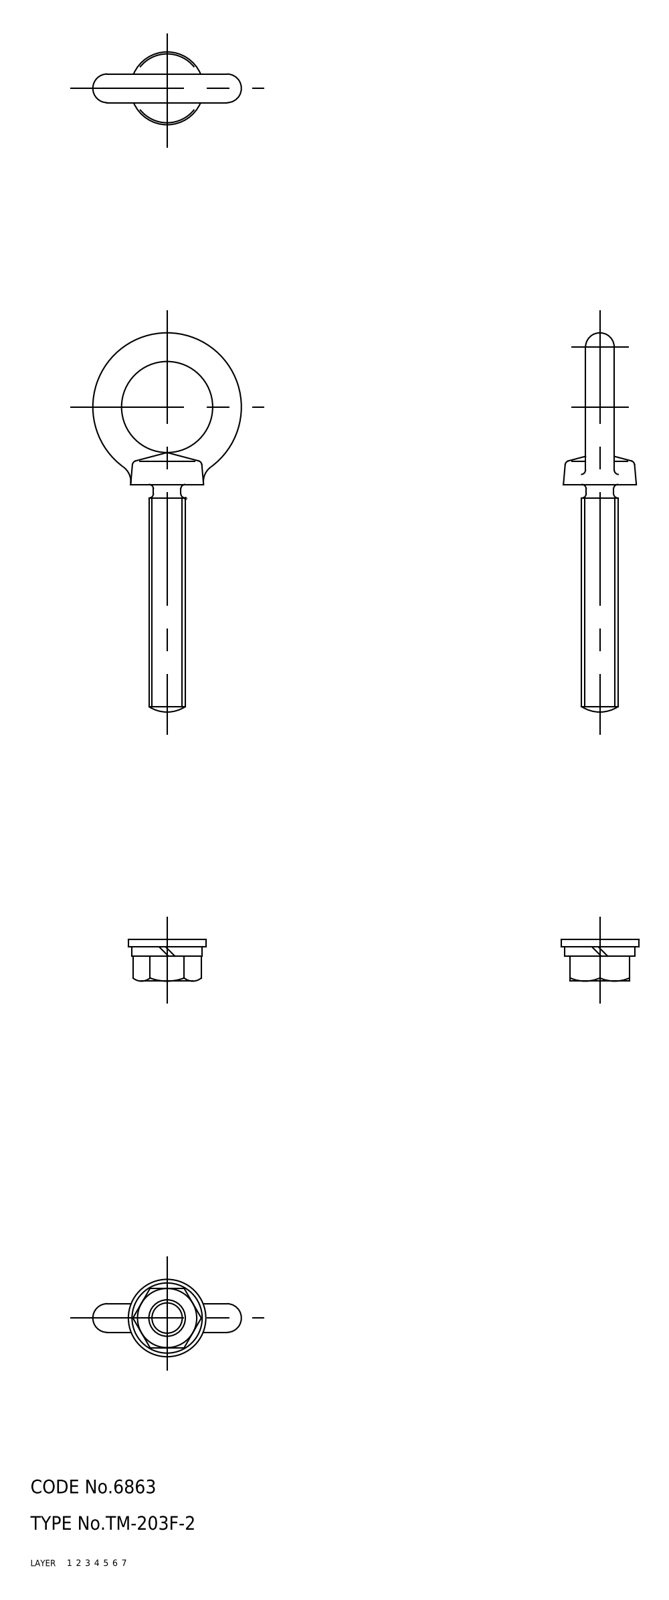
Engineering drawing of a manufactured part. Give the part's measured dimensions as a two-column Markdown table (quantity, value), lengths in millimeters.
| quantity | value |
| --- | --- |
| part name | TM_203F_2 |
| STEP written by | SolidWorks 2003240 (AUTOMOTIVE_DESIGN) |
| units | millimeters |
| bodies | 4 solids, 52 faces (13 planar, 12 cylindrical, 27 other) |
| overall size | 83.3 × 32.6 × 17 |
| volume | 6 878 mm³ |
| surface area | 4 658 mm² |
| round holes (diameter × count) | 8 × 1 |
| round bosses / shafts (diameter × count) | 17 × 1, 15.4 × 1 |
| main face-to-face distances | 1.6, 2, 3.6, 13, 5.5, 7.5, 9.1 |
